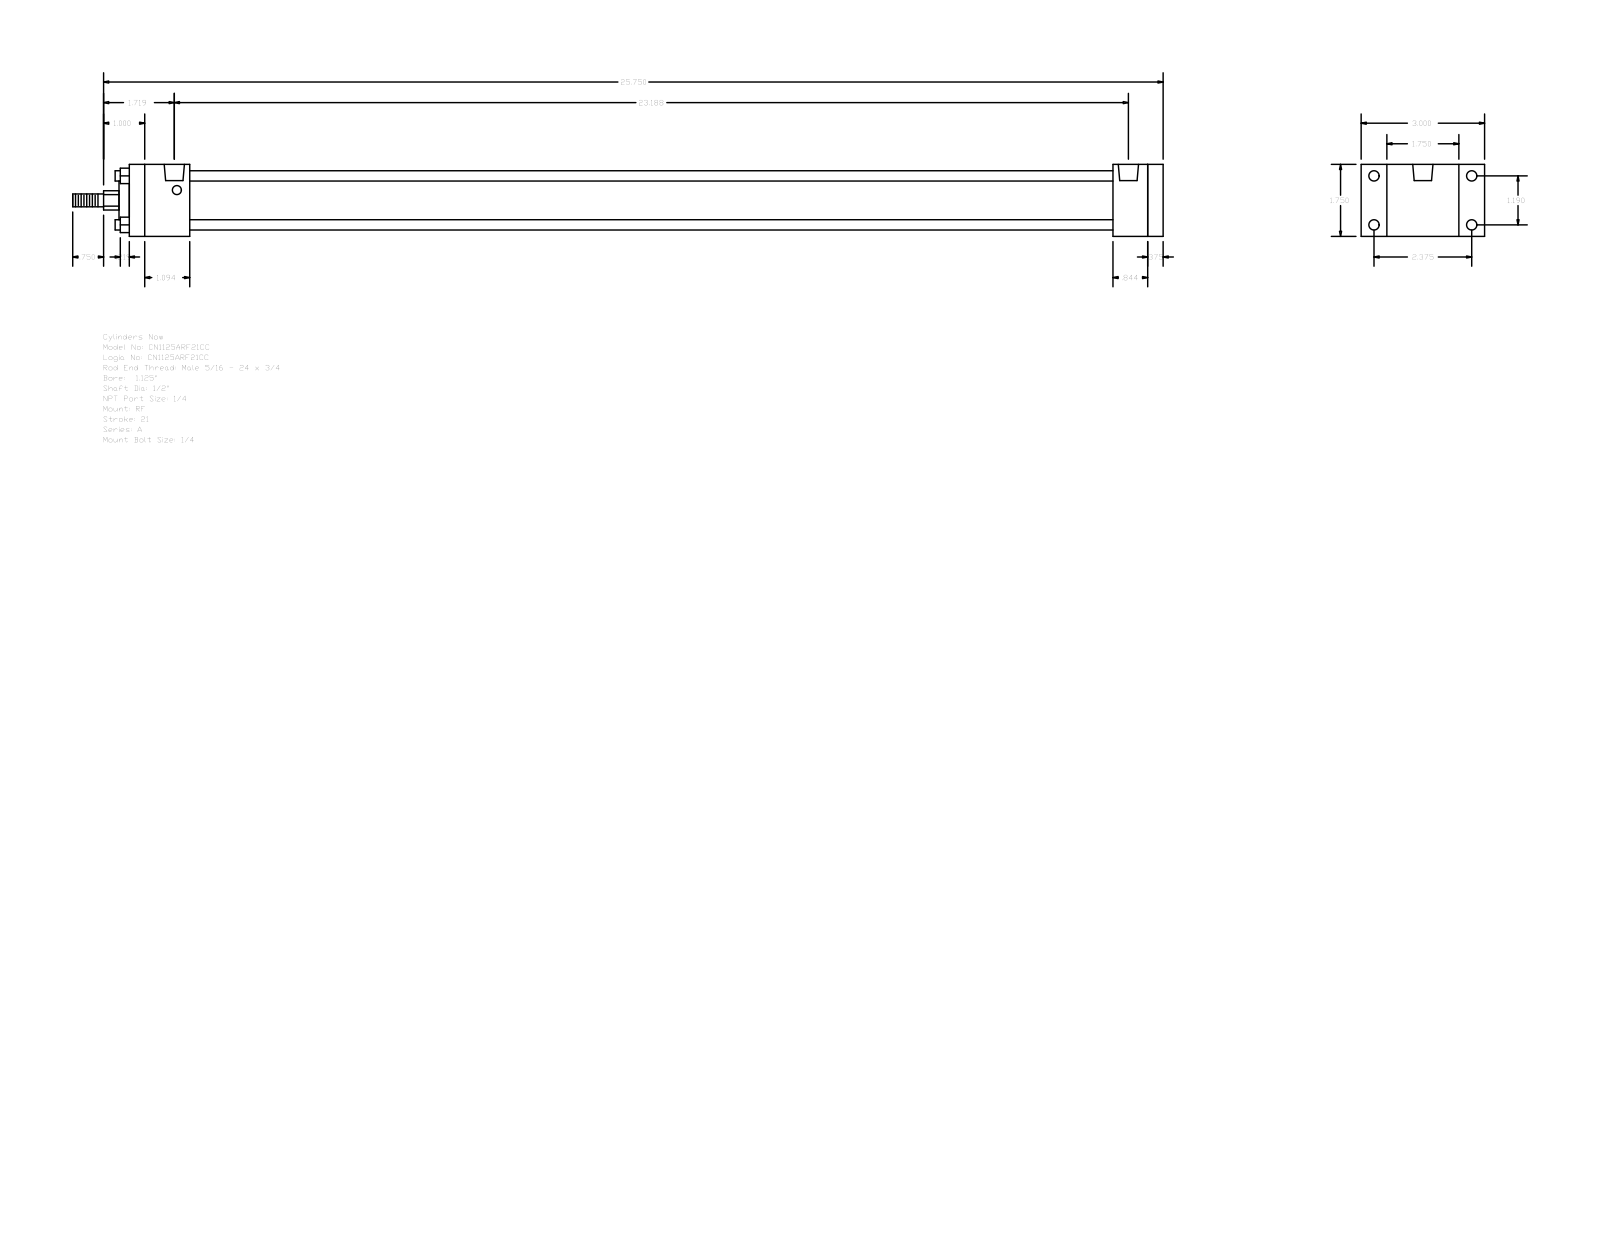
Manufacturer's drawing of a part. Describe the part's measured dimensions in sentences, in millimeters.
The part is named "A_RF__0112_0.5". Its 3-D file was written by "GSSL Pune (CONFIG_CONTROL_DESIGN)". It is 0 solids with 92 faces: 64 planar, 28 cylindrical and 0 other. Overall it measures 673.1 by 76.2 by 44.45 millimeters. Round holes: 4 of diameter 5.56, 4 of diameter 6.35, 2 of diameter 12.49. Round bosses or shafts: 4 of diameter 6.35, 1 of diameter 31.88, 1 of diameter 23.81, 1 of diameter 12.7, 1 of diameter 7.94. Partial cylindrical surfaces (rounded edges, fillets, slot ends): 1 of radius 5.94. The main face-to-face distances are 44.46, 9.53, 638.17, 628.64, 37.3, 607.21, 569.91, 591.34, 600.87, 21.43. The hole center spacings are 30.22, 60.32, 67.47, 585.79, 1.58, 1.59, 587.37, 587.38.
